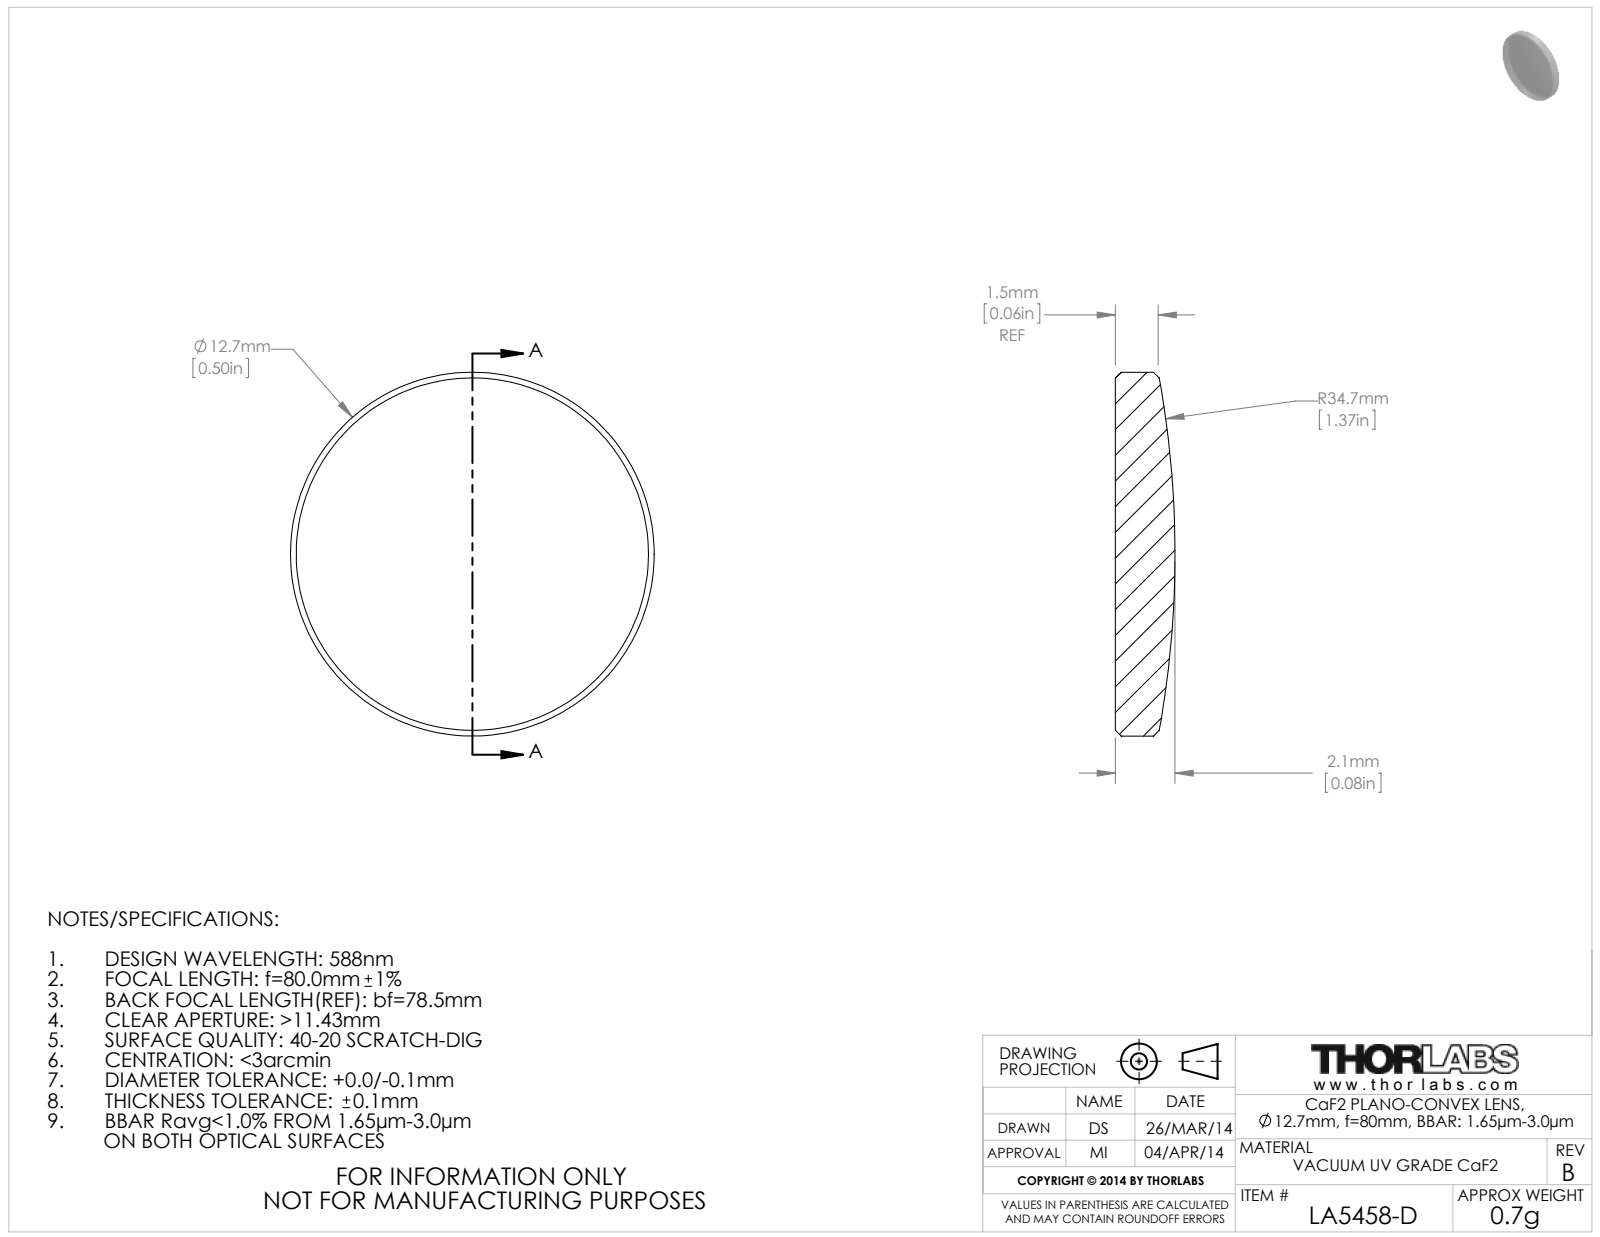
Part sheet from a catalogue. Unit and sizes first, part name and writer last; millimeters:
Units: millimetres
Overall size (bounding box): 12.7 × 12.7 × 2.08
Round bosses / shafts (diameter × count): ⌀12.7 ×1
Bodies: 0 solids, 5 faces (1 planar, 2 cylindrical, 2 other)
Part name (STEP PRODUCT): 22971-E0W
STEP written by: SolidWorks 2011 (AUTOMOTIVE_DESIGN)
